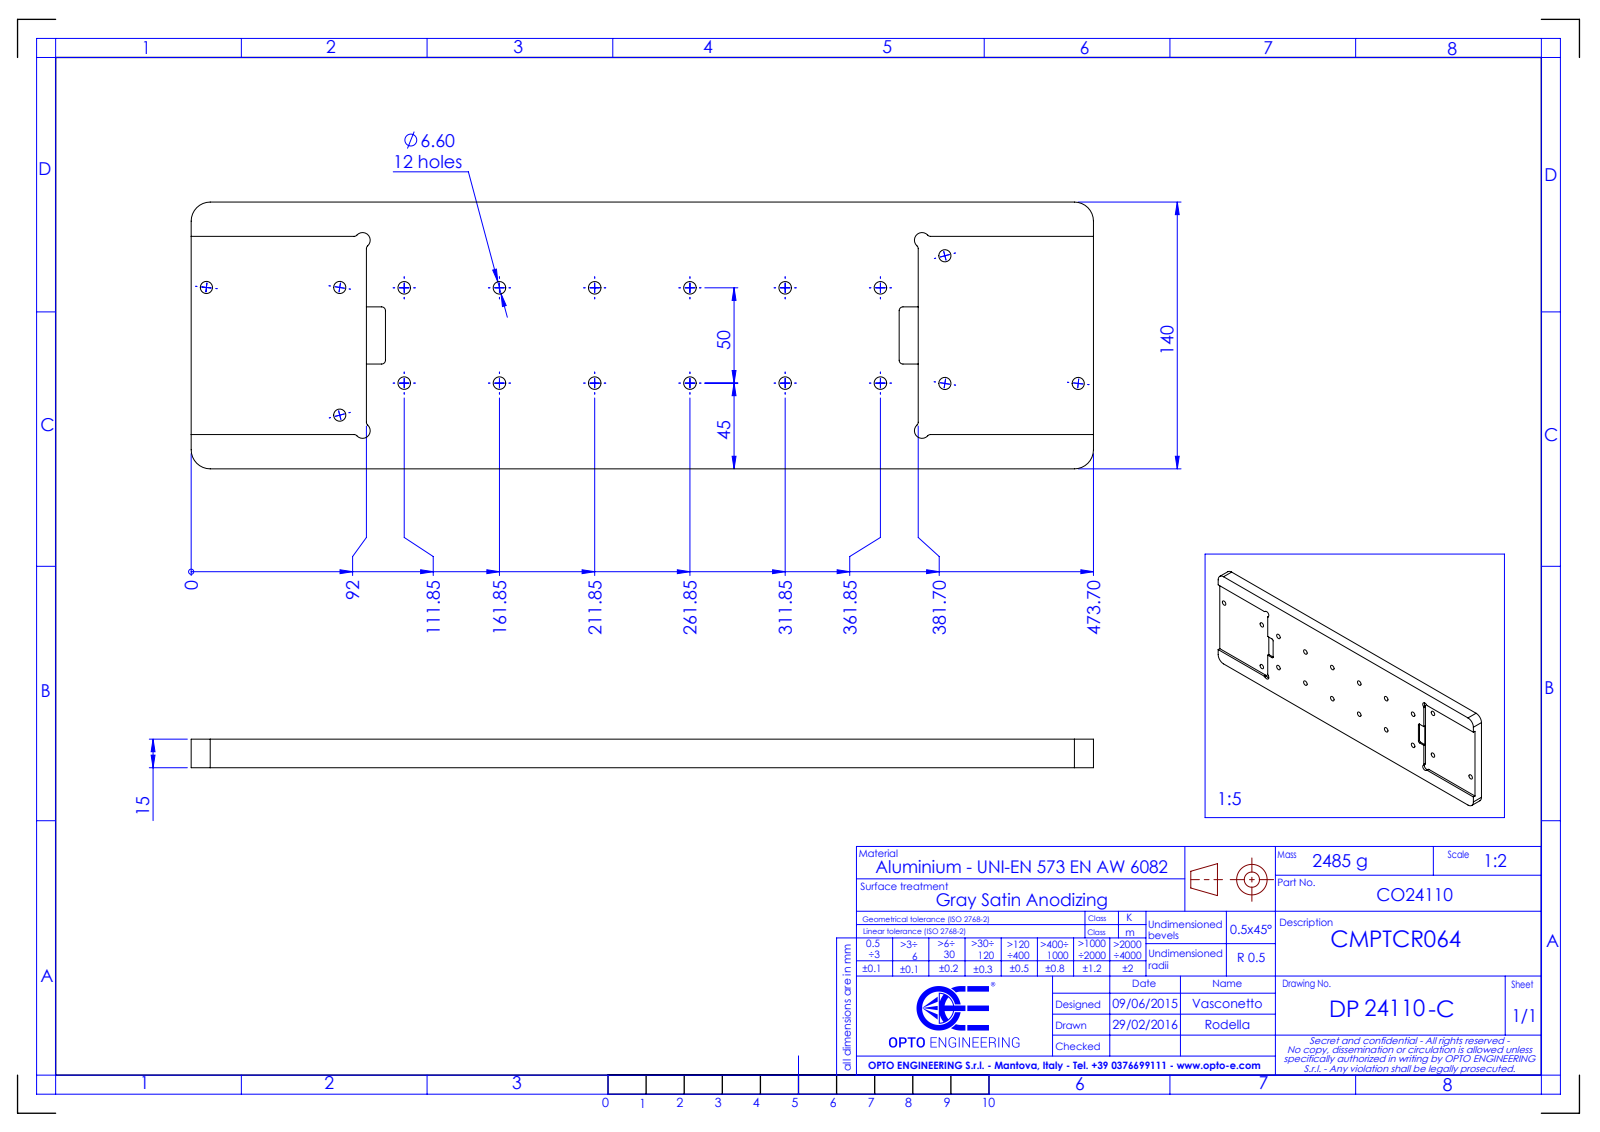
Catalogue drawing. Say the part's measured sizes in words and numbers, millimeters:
The part is named "DP24110". Its 3-D file was written by "SolidWorks 2021 (CONFIG_CONTROL_DESIGN)". It is 1 solid with 98 faces: 28 planar, 70 cylindrical and 0 other. Overall it measures 473.7 by 140 by 15 millimeters. Its volume is 923 769 cubic millimeters and its surface area 156 364 square millimeters. Round holes: 12 of diameter 6.6, 6 of diameter 6.4, 6 of diameter 11. Partial cylindrical surfaces (rounded edges, fillets, slot ends): 12 of radius 2, 4 of radius 4, 4 of radius 10. The main face-to-face distances are 15, 12, 3, 140, 473.7, 18, 122, 13, 1, 2. The hole center spacings are 50, 70.71, 100, 111.8, 150, 158.11, 200, 206.16.
